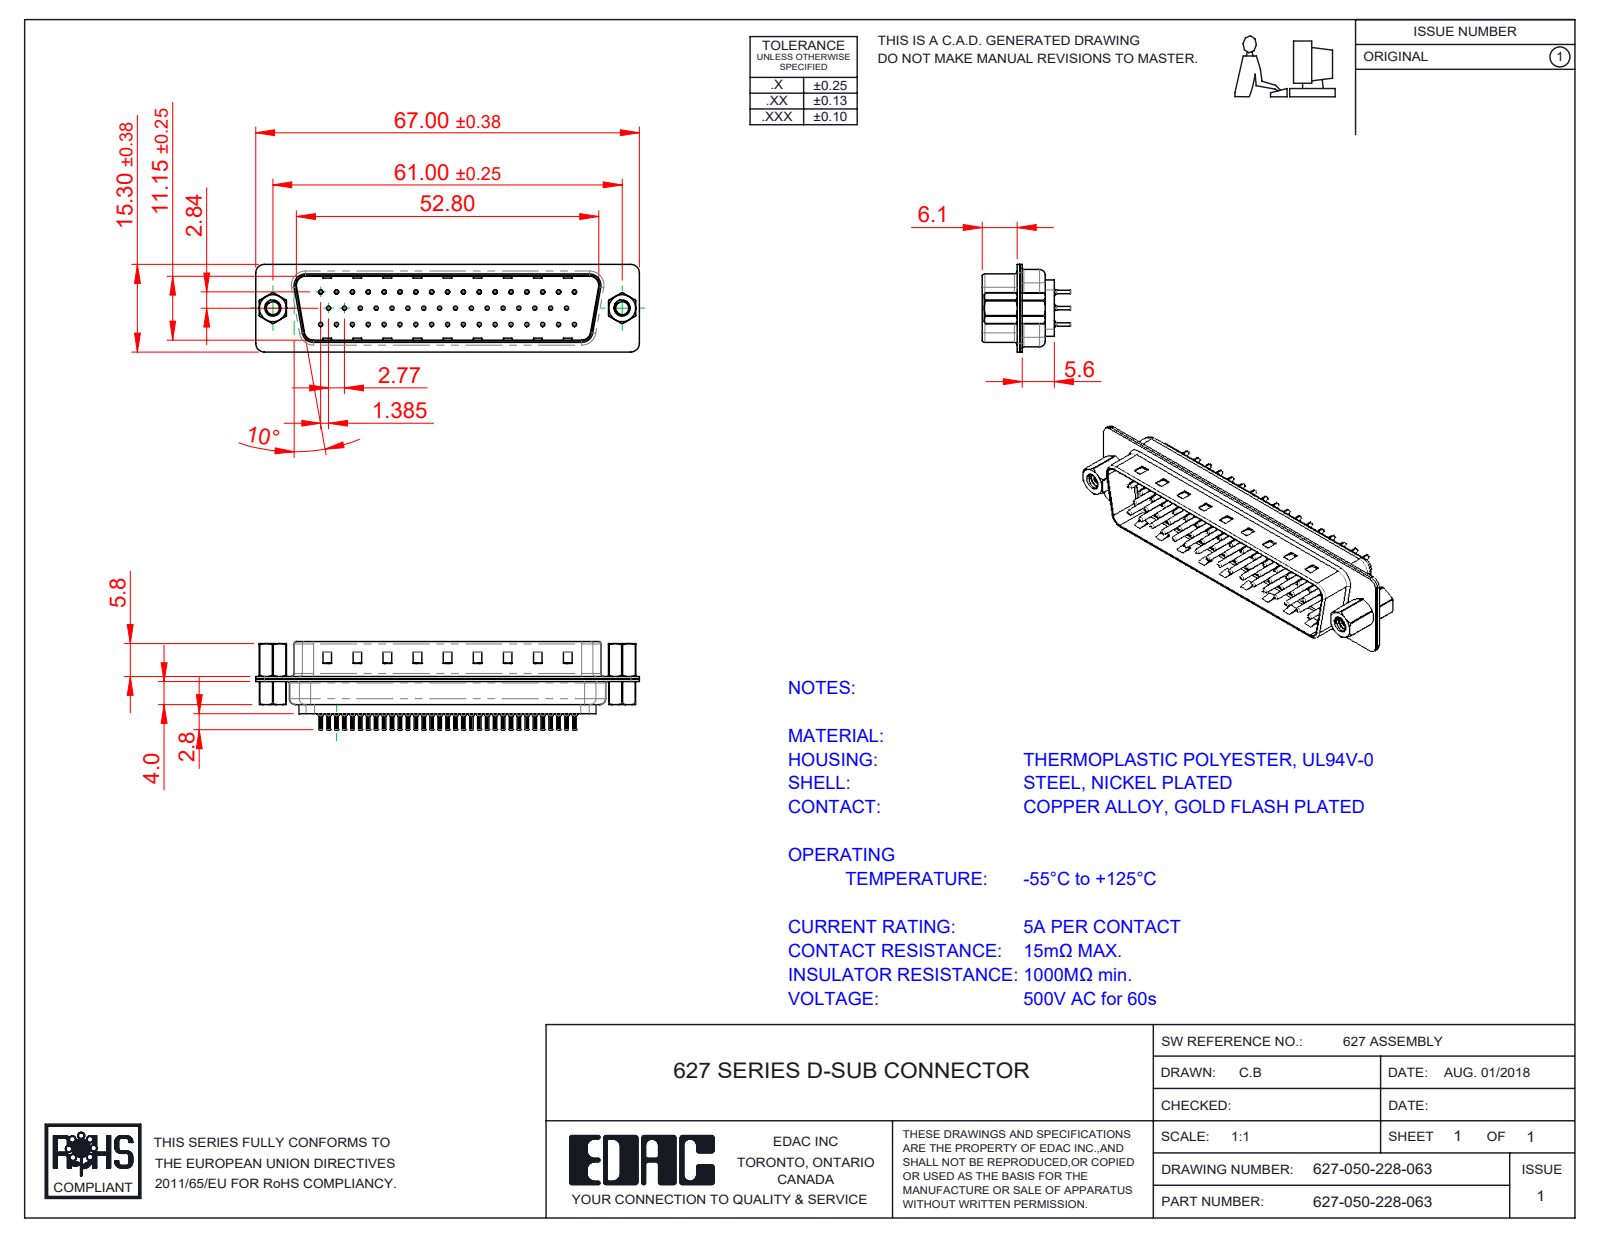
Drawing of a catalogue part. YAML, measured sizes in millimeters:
part_name: "627 4-40 Hex Standoff; 627 Shell Front_50 Contacts; 627 Contact Row 3_28L; 627 Housing_50 FF (+5 more)"
step_written_by: "SolidWorks 2020 (CONFIG_CONTROL_DESIGN)"
units: millimeters
bodies: {solids: 58, faces: 5545, planar: 1431, cylindrical: 2166, other: 1948}
overall_size: [67, 18.8, 15.3]
volume: 5762
surface_area: 15103
round_holes:
  - {diameter: 0.2, count: 50}
  - {diameter: 0.35, count: 50}
  - {diameter: 1.1, count: 50}
  - {diameter: 1.6, count: 50}
  - {diameter: 2.26, count: 2}
  - {diameter: 2.29, count: 2}
  - {diameter: 4, count: 2}
  - {diameter: 4.8, count: 2}
round_bosses_or_shafts:
  - {diameter: 2, count: 50}
  - {diameter: 1.5, count: 50}
  - {diameter: 0.75, count: 50}
  - {diameter: 0.6, count: 50}
  - {diameter: 5, count: 2}
  - {diameter: 4.9, count: 2}
  - {diameter: 2.79, count: 2}
partial_cylinders:
  - {radius: 0.1, count: 100}
  - {radius: 1.5, count: 16}
  - {radius: 2, count: 12}
  - {radius: 0.5, count: 8}
  - {radius: 1.6, count: 8}
  - {radius: 0.25, count: 4}
  - {radius: 0.6, count: 4}
  - {radius: 0.65, count: 4}
face_to_face_distances: [0.4, 6.05, 0.45, 11.55, 0.9, 2.8, 8.85, 6.5, 9.3, 0.78]
hole_center_spacings: [2.77, 3.16, 5.54, 8.31, 11.08, 13.85, 16.62, 19.39]
